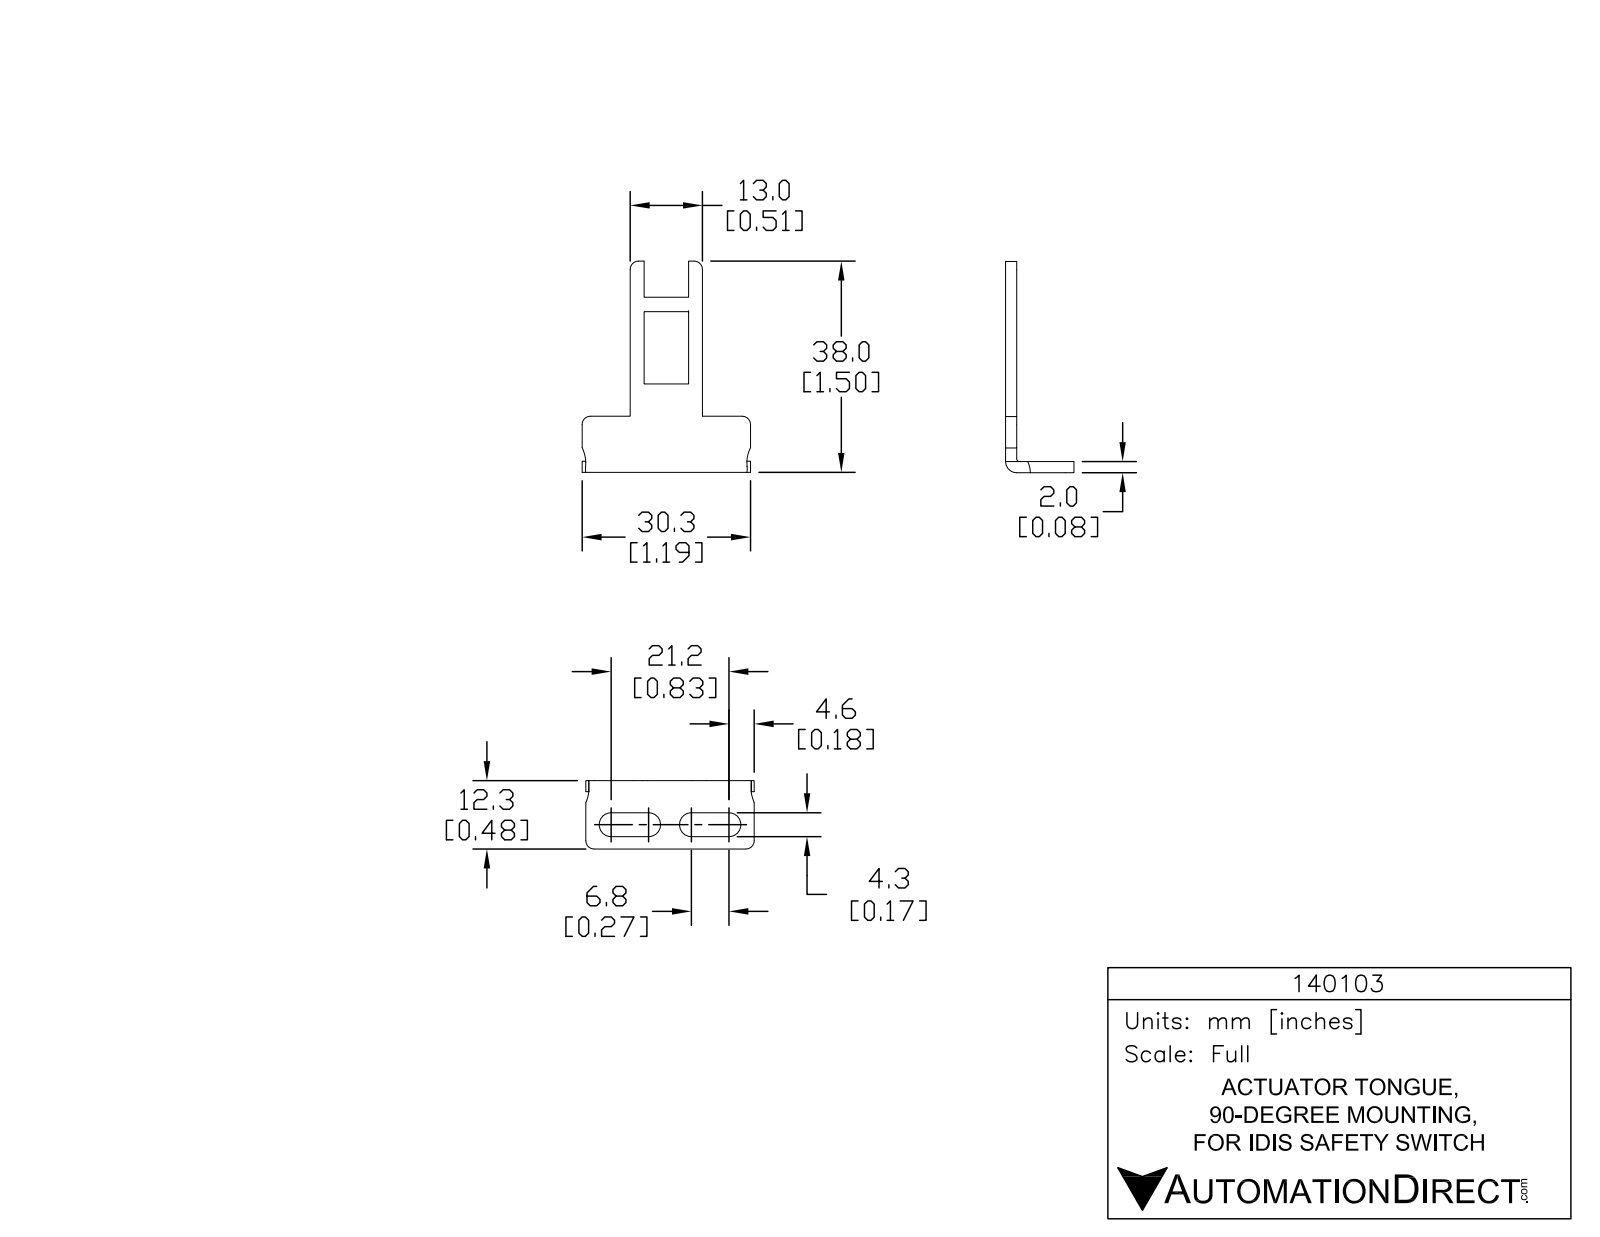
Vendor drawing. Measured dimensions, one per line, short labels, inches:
name: 140103
written by: SolidWorks 2017 (AUTOMOTIVE_DESIGN)
unit: in
bodies: 1 solid, 42 faces (26 planar, 14 cylindrical, 2 other)
size: 1.496 × 1.193 × 0.484
volume: 0.087 in³; area: 3.023 in²
rounds: 6× R0.059, 4× R0.085, 2× R0.246, 1× R0.02, 1× R0.079
face distances: 0.079, 0.098, 0.413, 0.512, 0.406, 0.484, 0.341, 0.439, 0.754, 0.852
